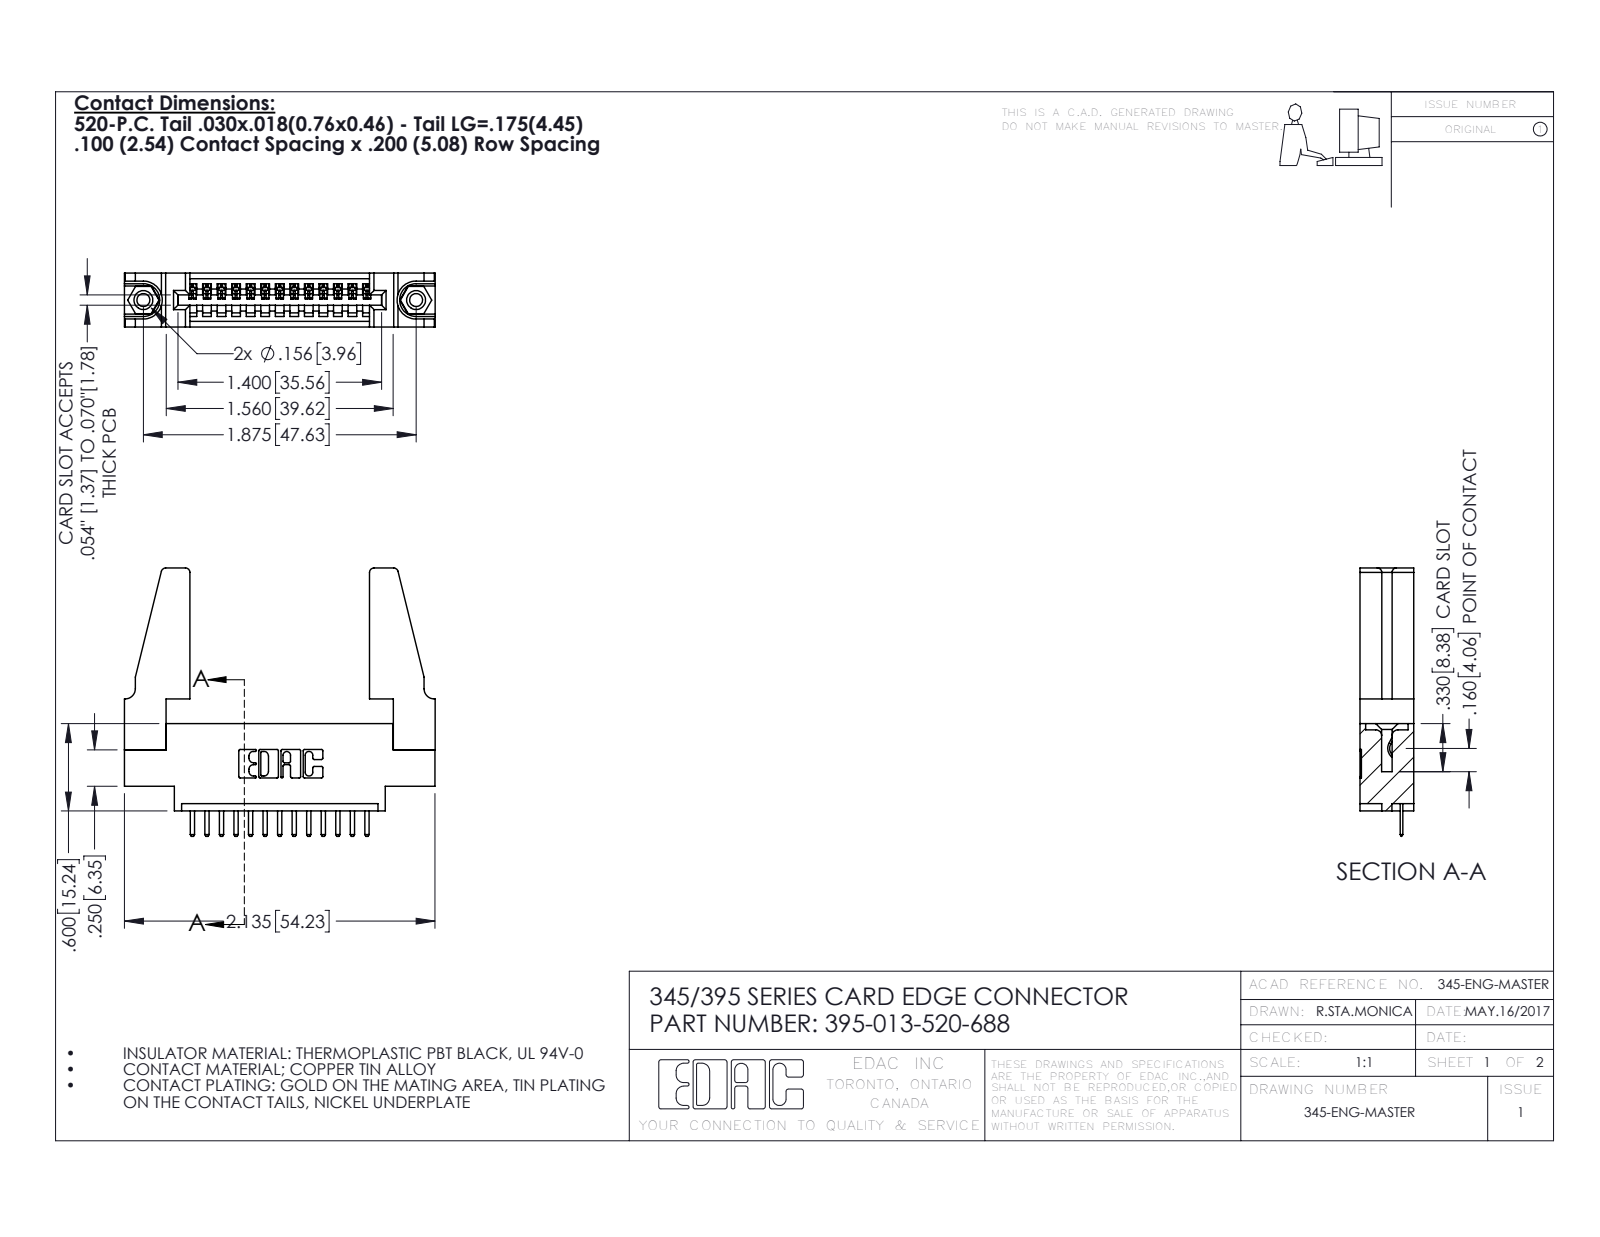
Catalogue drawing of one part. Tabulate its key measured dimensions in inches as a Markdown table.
| quantity | value |
| --- | --- |
| part name | 345 Part_0.170 Offset - 0.156 Dia-TH; 345-250-001_345-250-001-102; 345-292-001_345-293-120; 345-220-078_345-220-088 (+1 more) |
| STEP written by | SolidWorks 2016 (CONFIG_CONTROL_DESIGN) |
| units | inches |
| bodies | 18 solids, 1060 faces (702 planar, 342 cylindrical, 16 other) |
| overall size | 2.136 × 1.845 × 0.37 |
| volume | 0.489 in³ |
| surface area | 14.06 in² |
| round holes (diameter × count) | 0.089 × 2, 0.125 × 2, 0.156 × 2, 0.064 × 1 |
| round bosses / shafts (diameter × count) | 0.155 × 2 |
| partial cylindrical surfaces (radius × count) | 0.01 × 28, 0.006 × 26, 0.01 × 22, 0.03 × 8, 0.007 × 6, 0.031 × 6, 0.026 × 3, 0.031 × 2 |
| main face-to-face distances | 0.37, 0.072, 0.298, 0.2, 0.098, 0.272, 0.025, 0.225, 0.148, 0.15 |
| hole center spacings | 0.27, 1.643, 1.875 |
